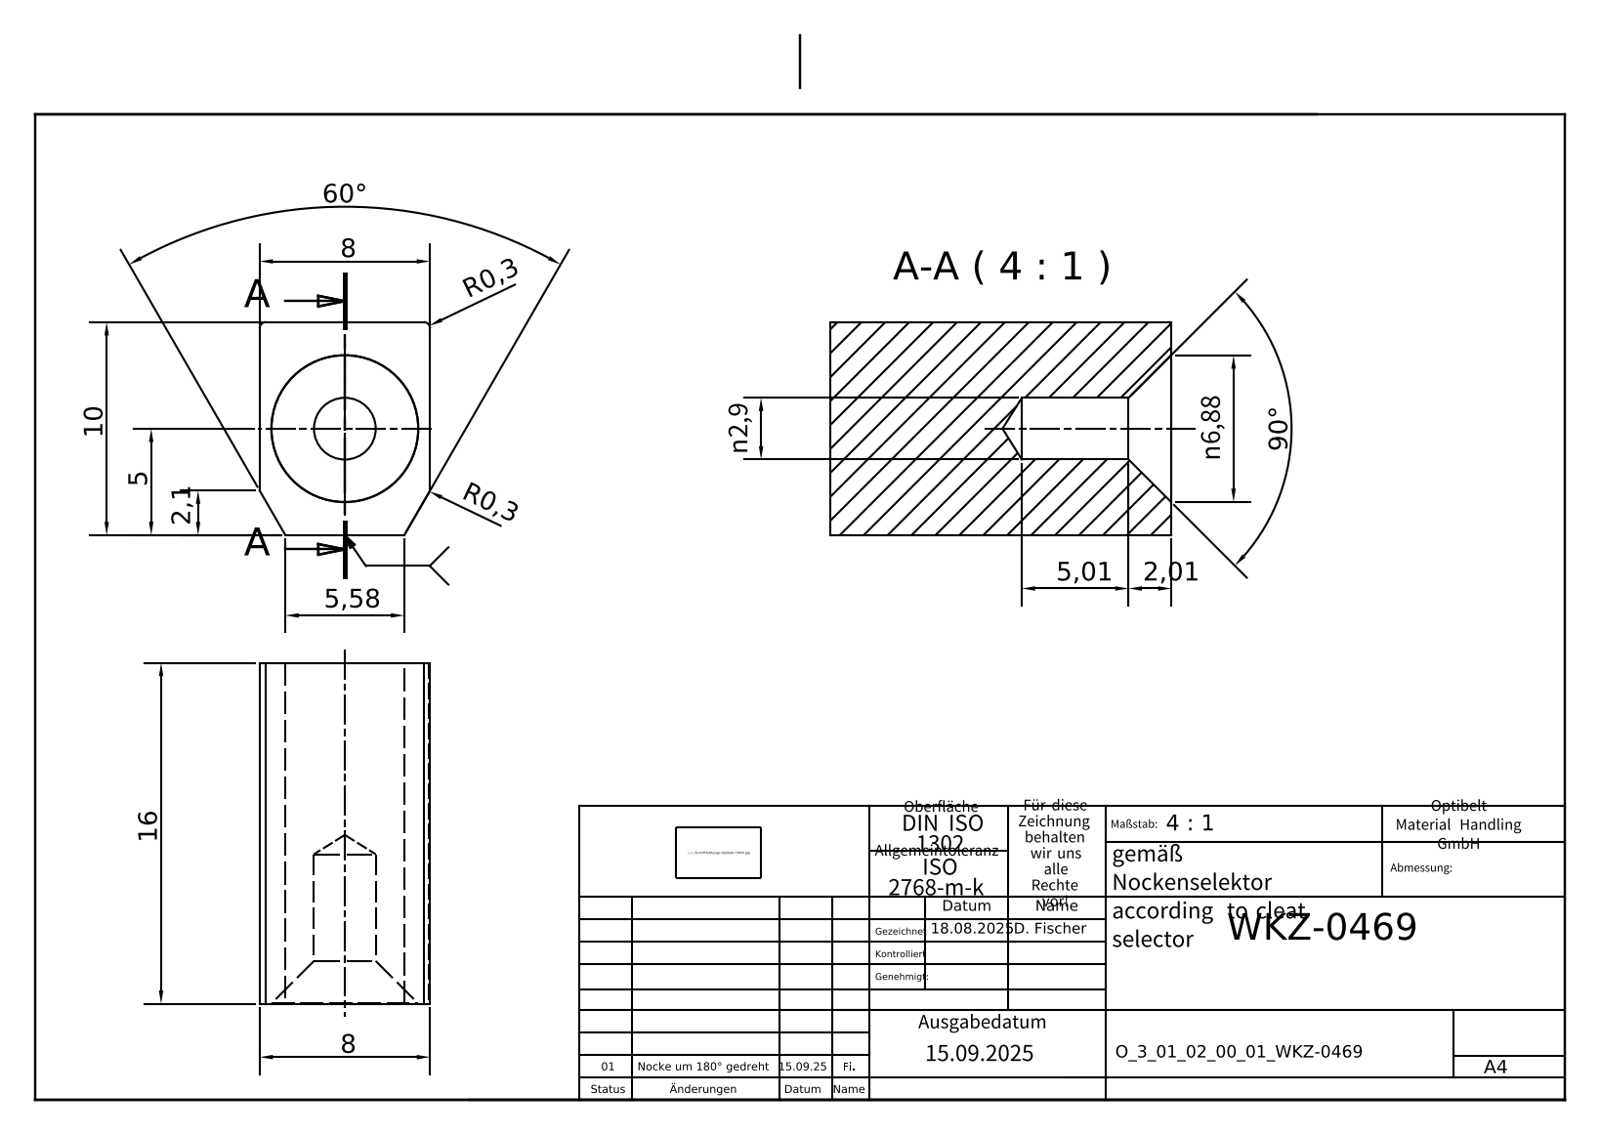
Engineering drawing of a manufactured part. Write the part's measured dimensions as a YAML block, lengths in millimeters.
part_name: "O_3_01_02_00_01_WKZ-0469"
step_written_by: "Autodesk Inventor 2025 (AUTOMOTIVE_DESIGN)"
units: millimeters
bodies: {solids: 1, faces: 16, planar: 9, cylindrical: 5, other: 2}
overall_size: [16, 10, 8]
volume: 1164
surface_area: 758
round_holes:
  - {diameter: 2.9, count: 1}
  - {diameter: 6.88, count: 1}
partial_cylinders:
  - {radius: 0.3, count: 3}
face_to_face_distances: [8, 10, 16]
